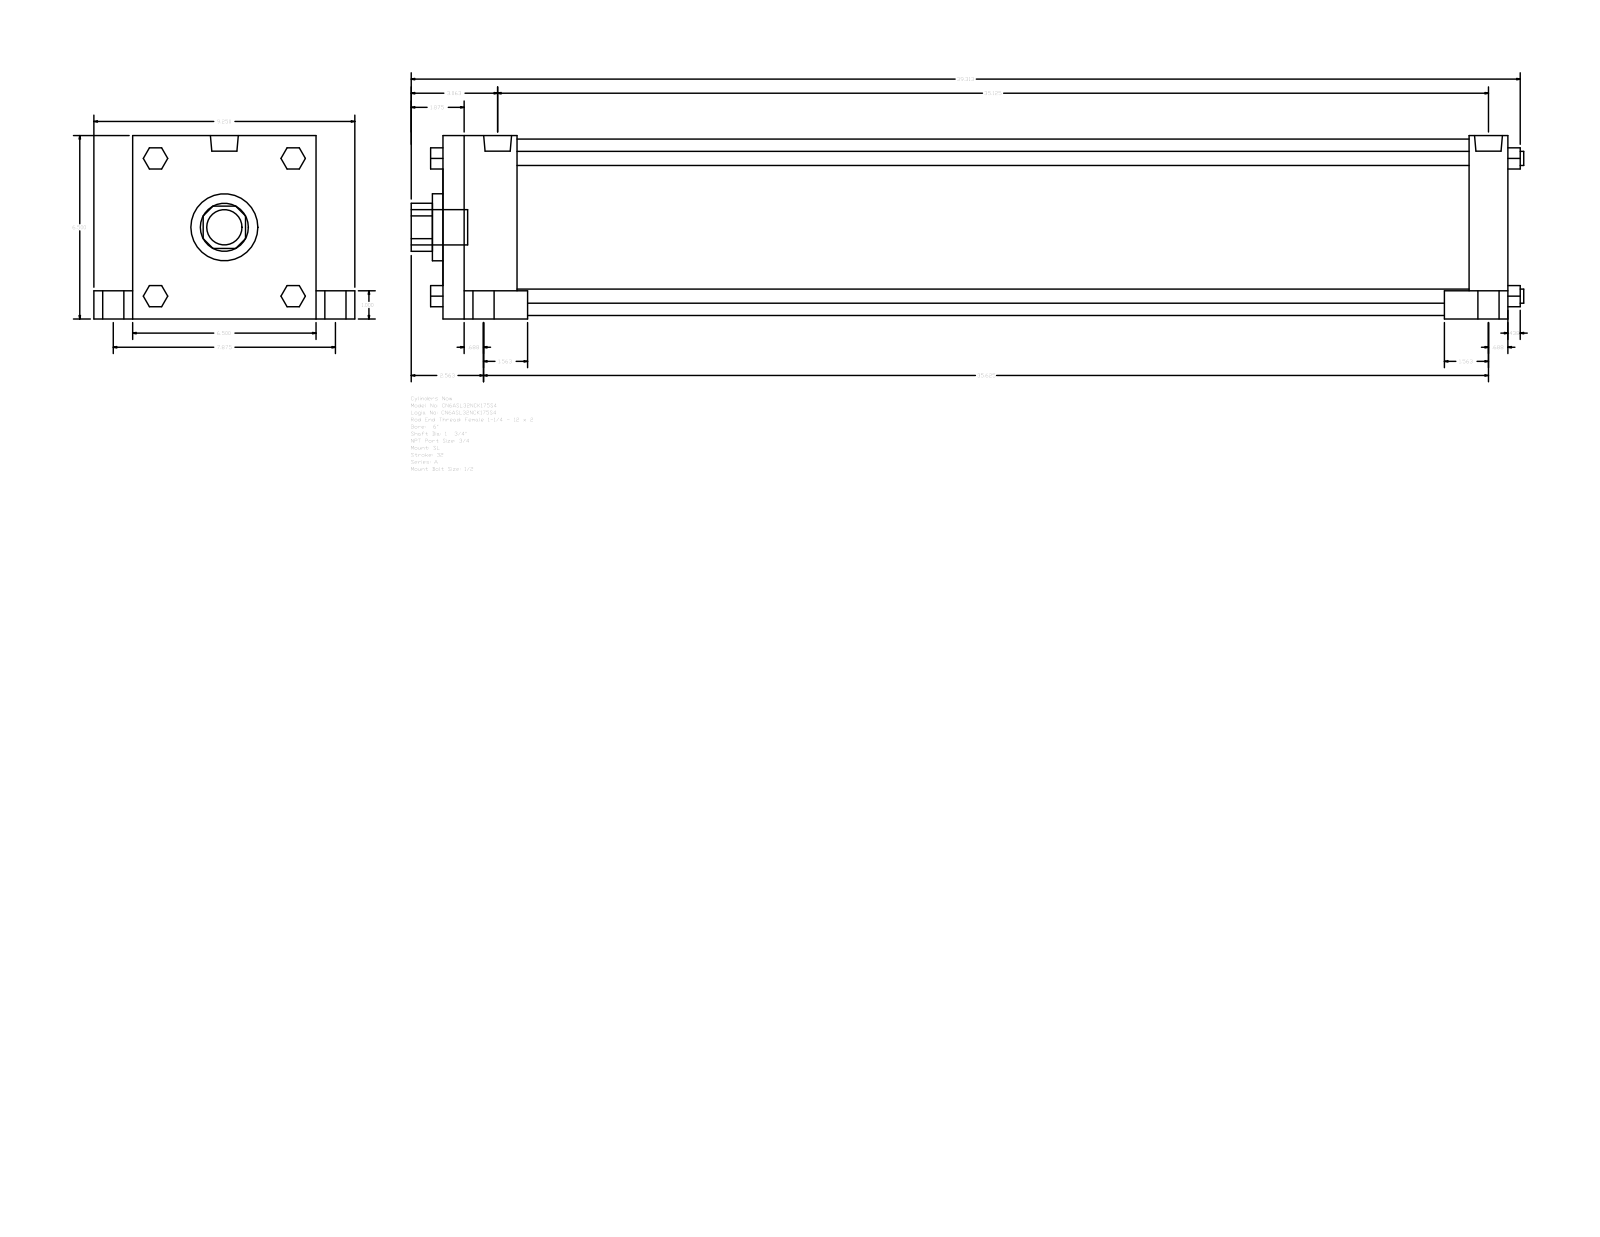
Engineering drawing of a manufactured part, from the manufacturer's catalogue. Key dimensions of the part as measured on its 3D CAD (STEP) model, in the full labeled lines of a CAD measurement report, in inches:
Part name (STEP PRODUCT): A_SL__0600_1.75
STEP written by: GSSL Pune (CONFIG_CONTROL_DESIGN)
Units: inches
Bodies: 0 solids, 150 faces (114 planar, 36 cylindrical, 0 other)
Overall size (bounding box): 39.437 × 9.25 × 6.5
Round holes (diameter × count): ⌀1.75 ×1, ⌀2.375 ×1, ⌀6.25 ×1
Round bosses / shafts (diameter × count): ⌀1 ×4, ⌀0.75 ×4, ⌀0.594 ×4, ⌀0.5 ×4, ⌀0.989 ×2, ⌀1.25 ×1
Partial cylindrical surfaces — rounded edges, fillets, slot ends (radius × count): R0.852 ×1
Main face-to-face distances: 6.5, 37.75, 1.375, 2.625, 35.125, 36.375, 33.75, 1, 5.5, 7.875
